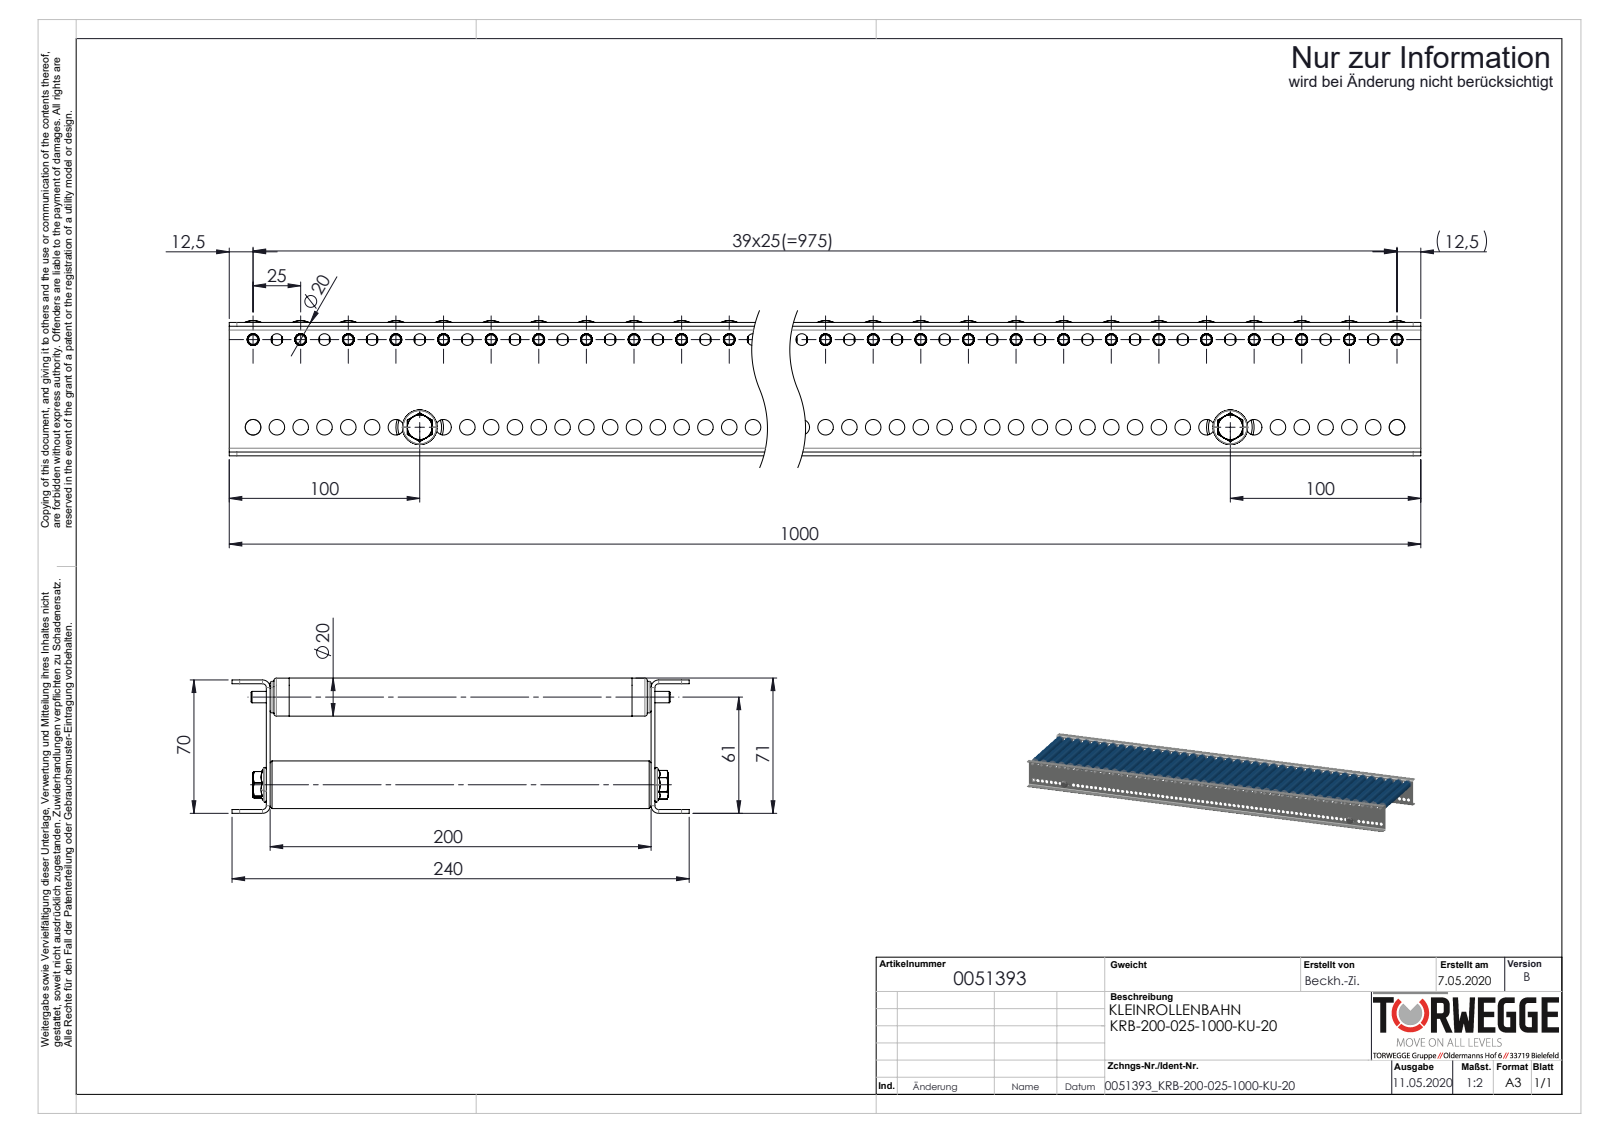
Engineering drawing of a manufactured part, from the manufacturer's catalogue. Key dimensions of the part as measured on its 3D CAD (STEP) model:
Part name (STEP PRODUCT): Profil_KRB-20x70x20x2_KFG_S100204_U-PROFIL-20-70-20-2-KRB-20-L=1000; S100994_Sperrzahnschraube_M08x16-8.8-A2K; 0051393; 0039777_Achse-Ø06-FA-KFG_L=220 fr D20 (+4 more)
STEP written by: SolidWorks 2020 (AUTOMOTIVE_DESIGN)
Units: millimetres
Bodies: 252 solids, 10672 faces (3560 planar, 3968 cylindrical, 3144 other)
Overall size (bounding box): 1000 × 240 × 71
Volume: 1 624 000 mm³ · Surface area: 1 834 000 mm²
Round holes (diameter × count): ⌀6.2 ×79, ⌀8.2 ×79, ⌀6.1 ×40, ⌀12.4 ×40, ⌀13.2 ×40, ⌀14.6 ×40, ⌀16.2 ×40, ⌀17 ×40, ⌀17.2 ×40, ⌀6.8 ×2, ⌀21 ×2
Round bosses / shafts (diameter × count): ⌀20 ×40, ⌀19.9 ×40, ⌀17.1 ×40, ⌀16.8 ×40, ⌀16.5 ×40, ⌀11.4 ×40, ⌀11.1 ×40, ⌀10.2 ×40
Partial cylindrical surfaces — rounded edges, fillets, slot ends (radius × count): R4.05 ×40, R4 ×8, R2 ×4
Main face-to-face distances: 2, 202, 68, 200, 204, 66, 70, 192, 10, 12
Hole centre spacings: 12.5, 25, 37.5, 50, 62.5, 75, 87.5, 100
